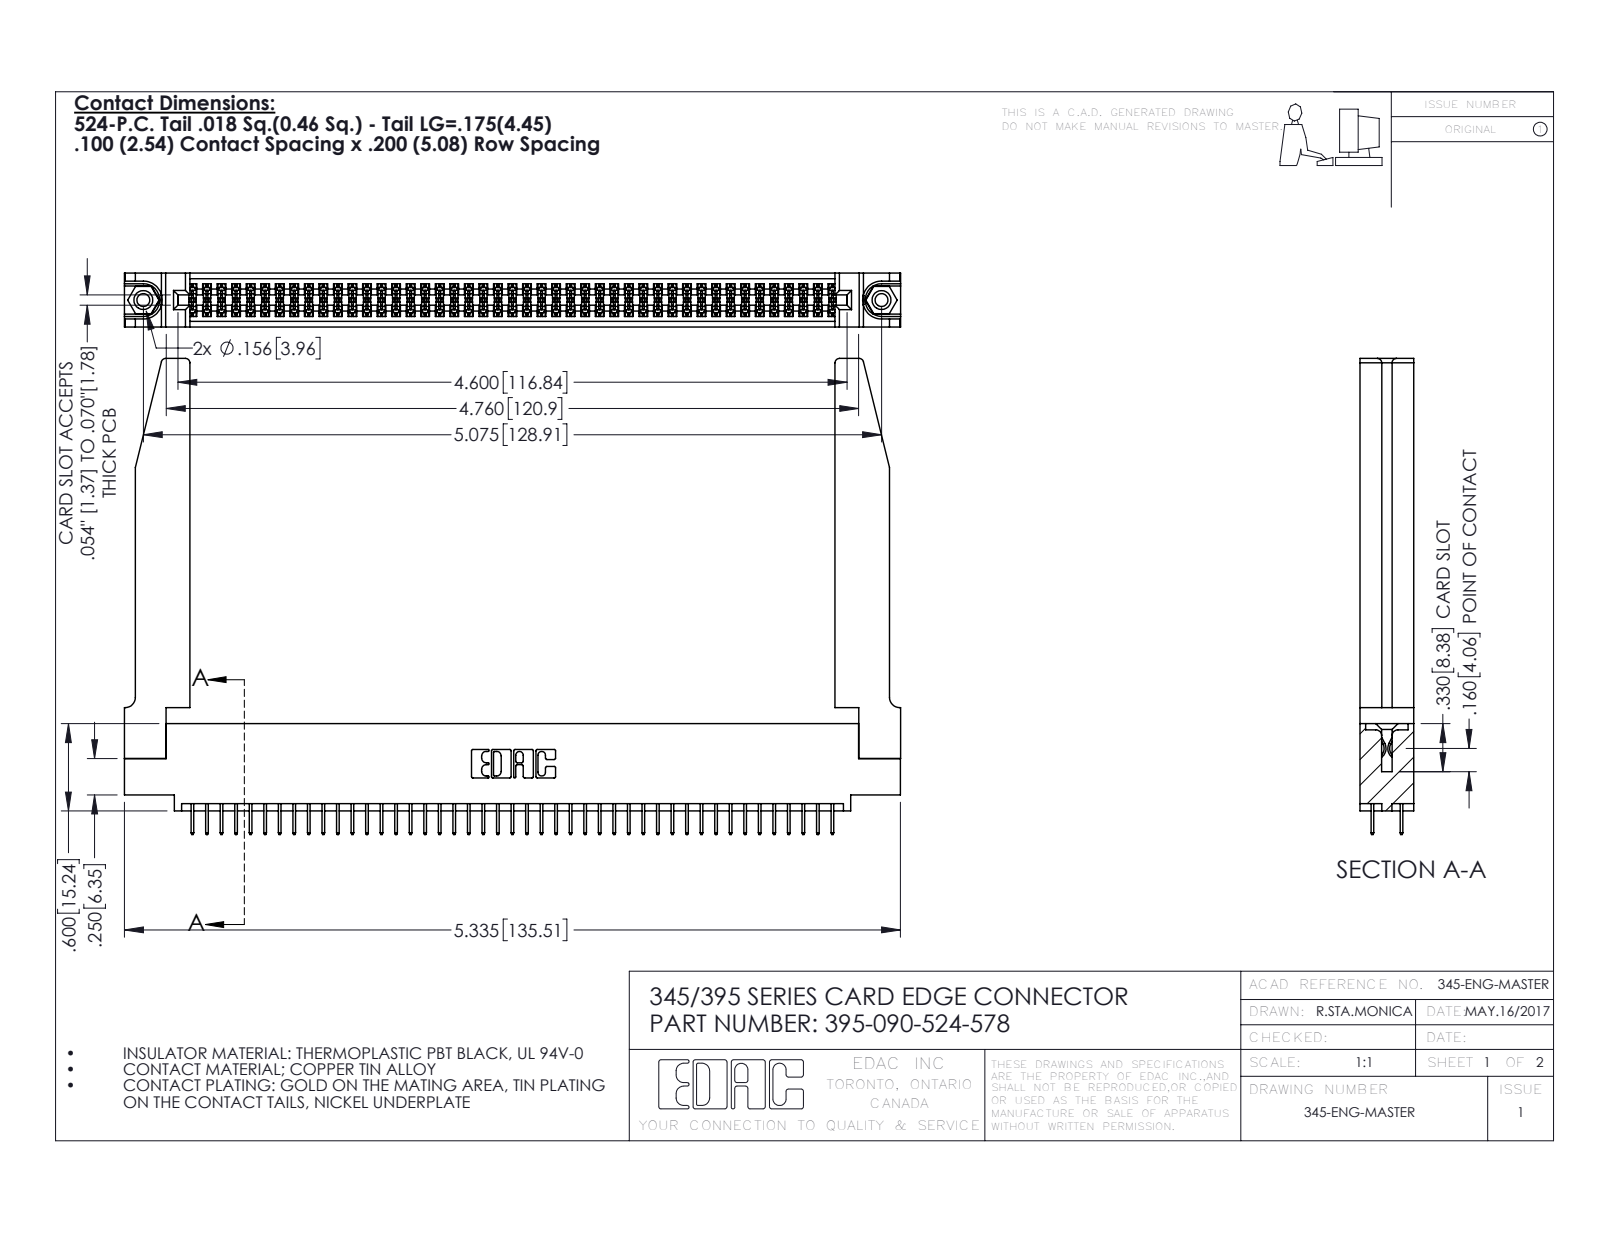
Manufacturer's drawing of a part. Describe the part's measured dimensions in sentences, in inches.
The part is named "345-292-001_345-293-124; 395-090-524-578; 345-250-001_345-250-001-102; 345 Part_0.110 Offset - 0.156 Dia-TH (+1 more)". Its 3-D file was written by "SolidWorks 2016 (CONFIG_CONTROL_DESIGN)". It is 95 solids with 5224 faces: 3736 planar, 1436 cylindrical and 52 other. Overall it measures 5.336 by 3.272 by 0.37 inches. Its volume is 1.267 cubic inches and its surface area 40.03 square inches. Round holes: 2 of diameter 0.089, 2 of diameter 0.125, 2 of diameter 0.156, 1 of diameter 0.064. Round bosses or shafts: 2 of diameter 0.155. Partial cylindrical surfaces (rounded edges, fillets, slot ends): 135 of radius 0.006, 22 of radius 0.01, 8 of radius 0.03, 6 of radius 0.007, 6 of radius 0.031, 3 of radius 0.026, 2 of radius 0.014, 2 of radius 0.019. The main face-to-face distances are 0.37, 0.072, 0.298, 0.2, 0.098, 0.272, 0.025, 0.225, 0.148, 0.15. The hole center spacings are 0.27, 4.839, 5.075.
